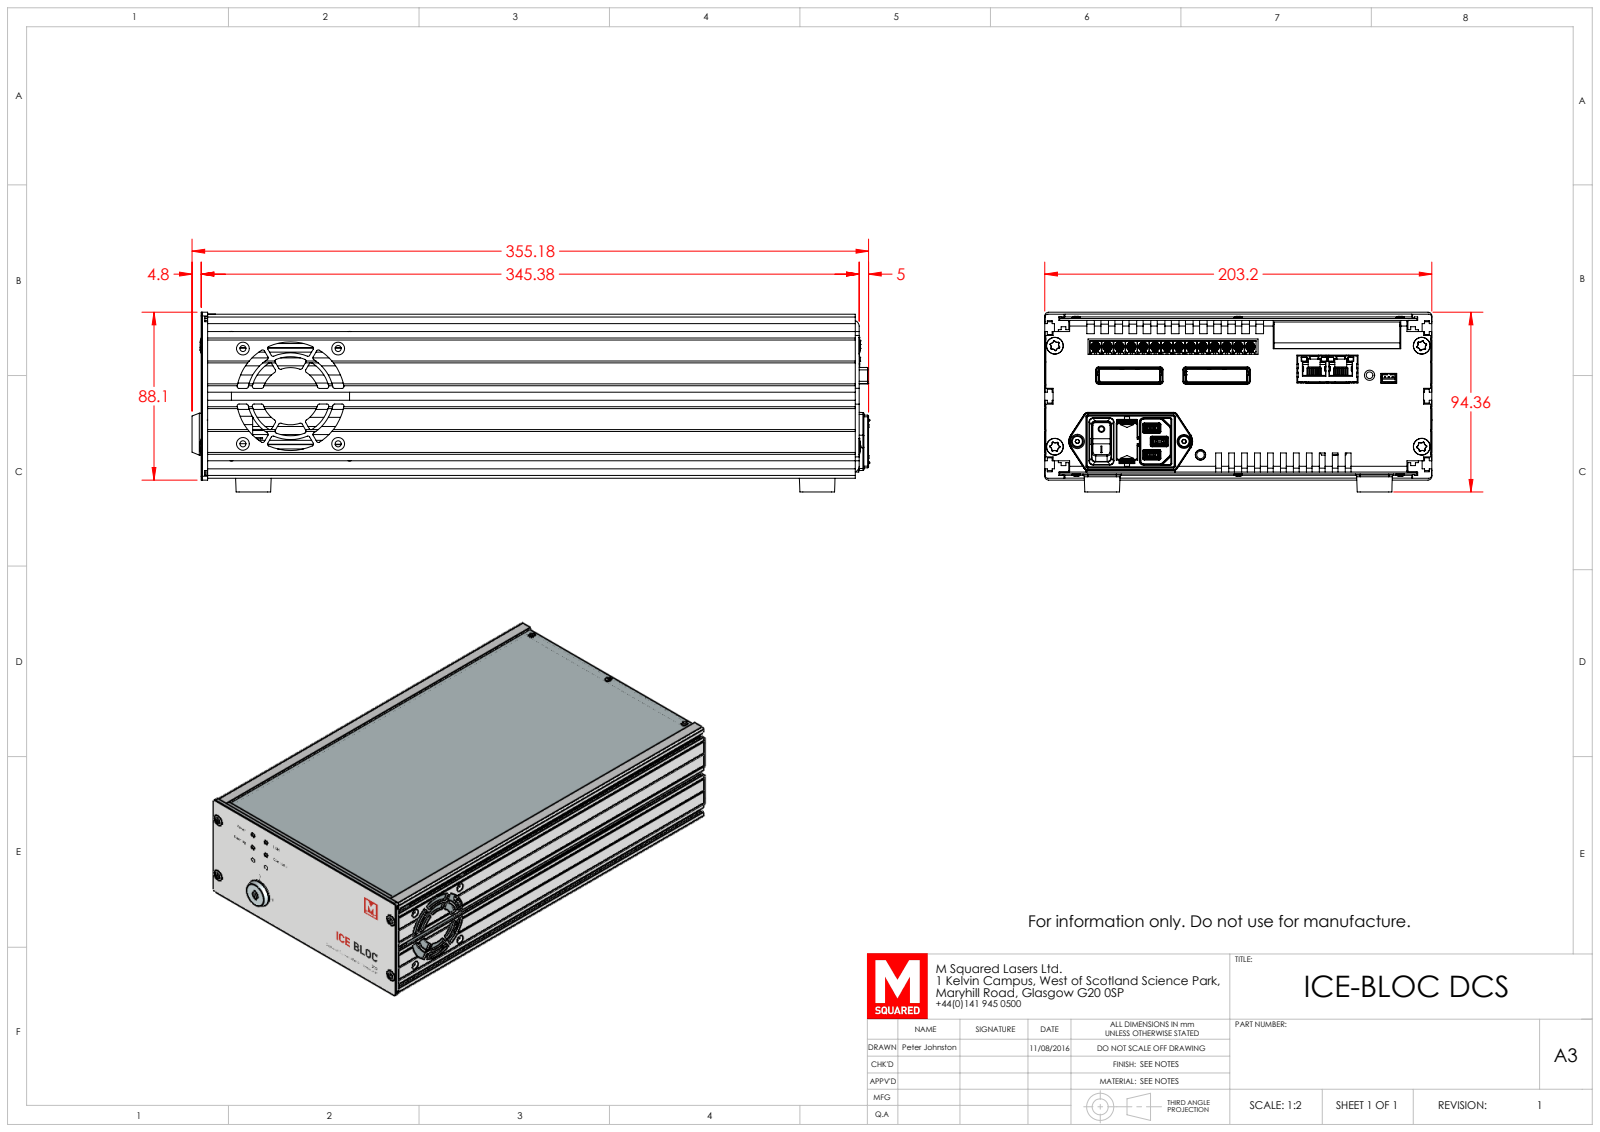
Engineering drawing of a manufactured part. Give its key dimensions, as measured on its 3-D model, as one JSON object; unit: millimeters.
{"part_name": "ICE-BLOC DCS", "step_written_by": "SolidWorks 2015 (AUTOMOTIVE_DESIGN)", "units": "millimeters", "bodies": {"solids": 0, "faces": 1942, "planar": 1062, "cylindrical": 593, "other": 287}, "overall_size": [355.77, 203.2, 94.36], "round_holes": [[3.42, 14], [3.2, 4], [3.5, 4], [9, 4], [0.95, 3], [2, 3], [6.3, 2], [2.5, 1], [5.4, 1], [7.3, 1], [7.5, 1]], "round_bosses_or_shafts": [[4.9, 14], [4.4, 3], [2.4, 3], [5.35, 2], [22, 1], [4, 1], [3.5, 1]], "partial_cylinders_radius": [[1, 50], [2, 48], [0.2, 43], [0.5, 31], [1.16, 20], [2.5, 16], [2, 14], [1.5, 13]], "face_to_face_distances": [1, 80.56, 81.56, 79.56, 203, 3, 12.5, 190.5, 0.38, 3.38], "hole_center_spacings": [6.25, 12.5, 18.75, 25, 50, 31.25, 37.5, 43.75]}
